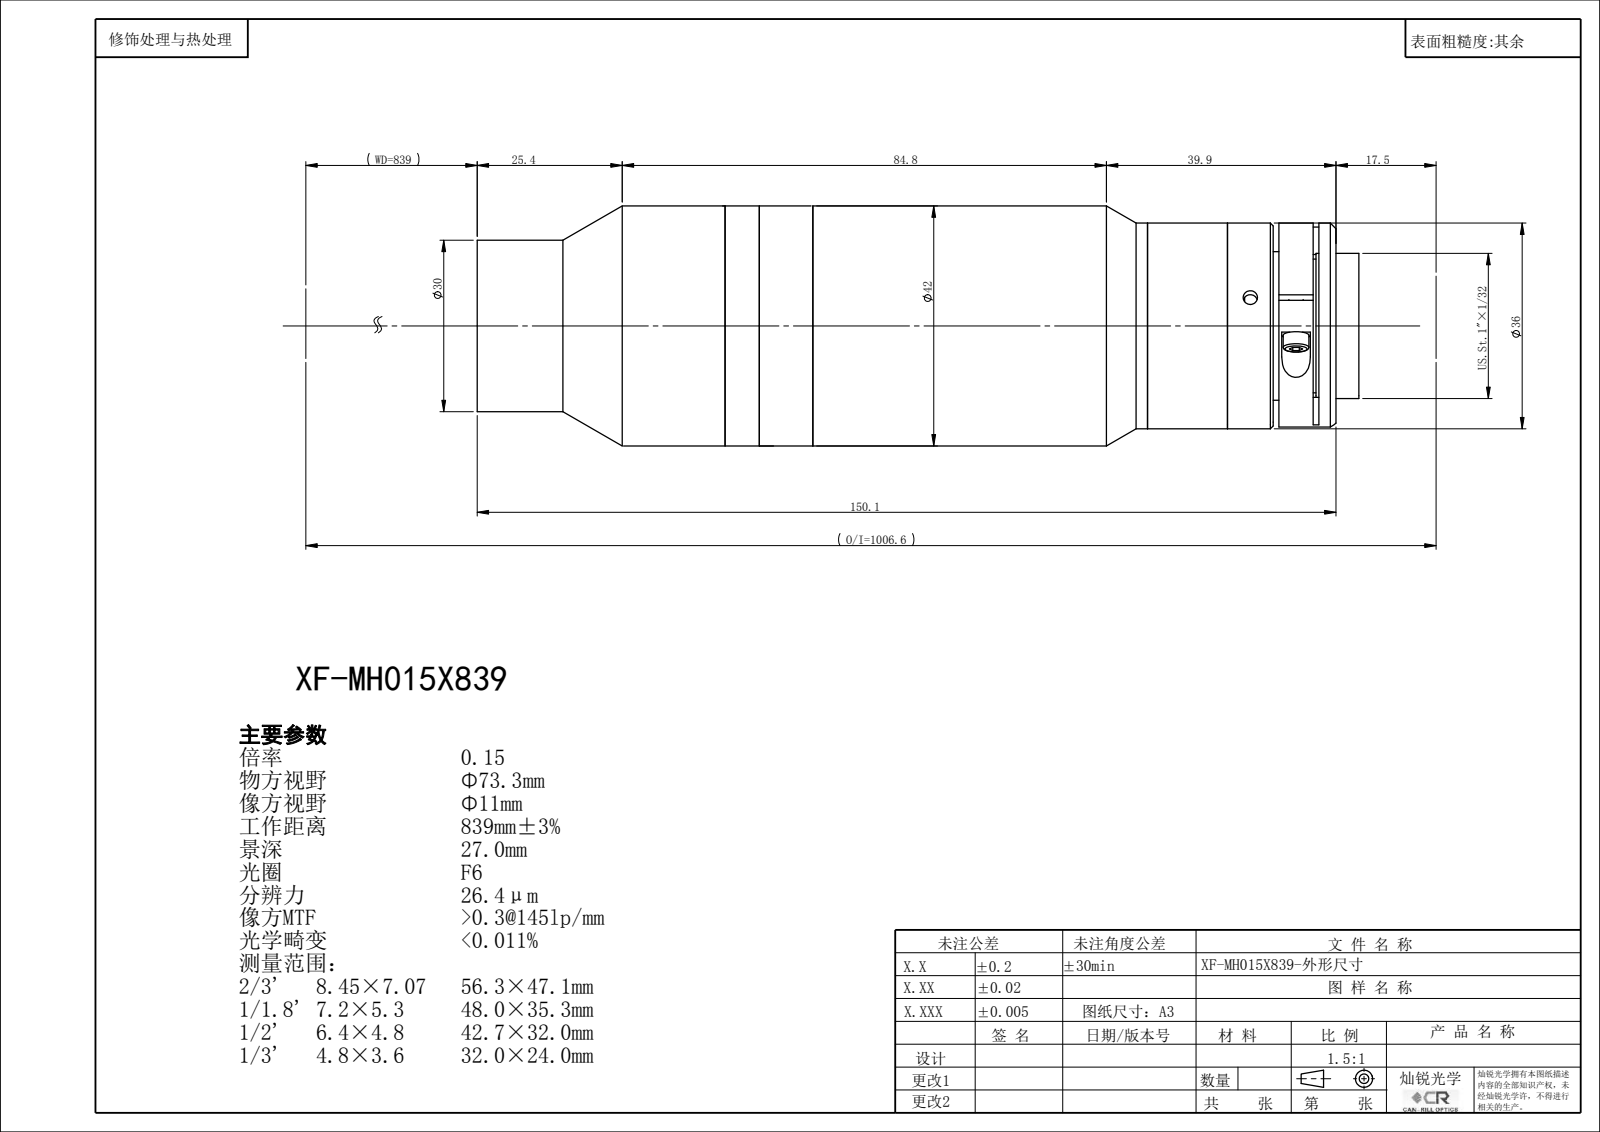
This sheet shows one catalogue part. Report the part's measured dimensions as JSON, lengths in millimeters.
{"part_name": "XF-MH015X839", "step_written_by": "SolidWorks 2022 (CONFIG_CONTROL_DESIGN)", "units": "millimeters", "bodies": {"solids": 0, "faces": 128, "planar": 66, "cylindrical": 40, "other": 22}, "overall_size": [154.02, 42, 42], "round_holes": [[2.5, 3], [22.4, 1], [24, 1], [26.4, 1]], "round_bosses_or_shafts": [[42, 1], [36, 1], [34, 1], [30, 1], [25.4, 1]], "face_to_face_distances": [18.67, 1.5, 17.17, 14, 31.17, 32.67, 6, 20, 11.17, 12.67]}
